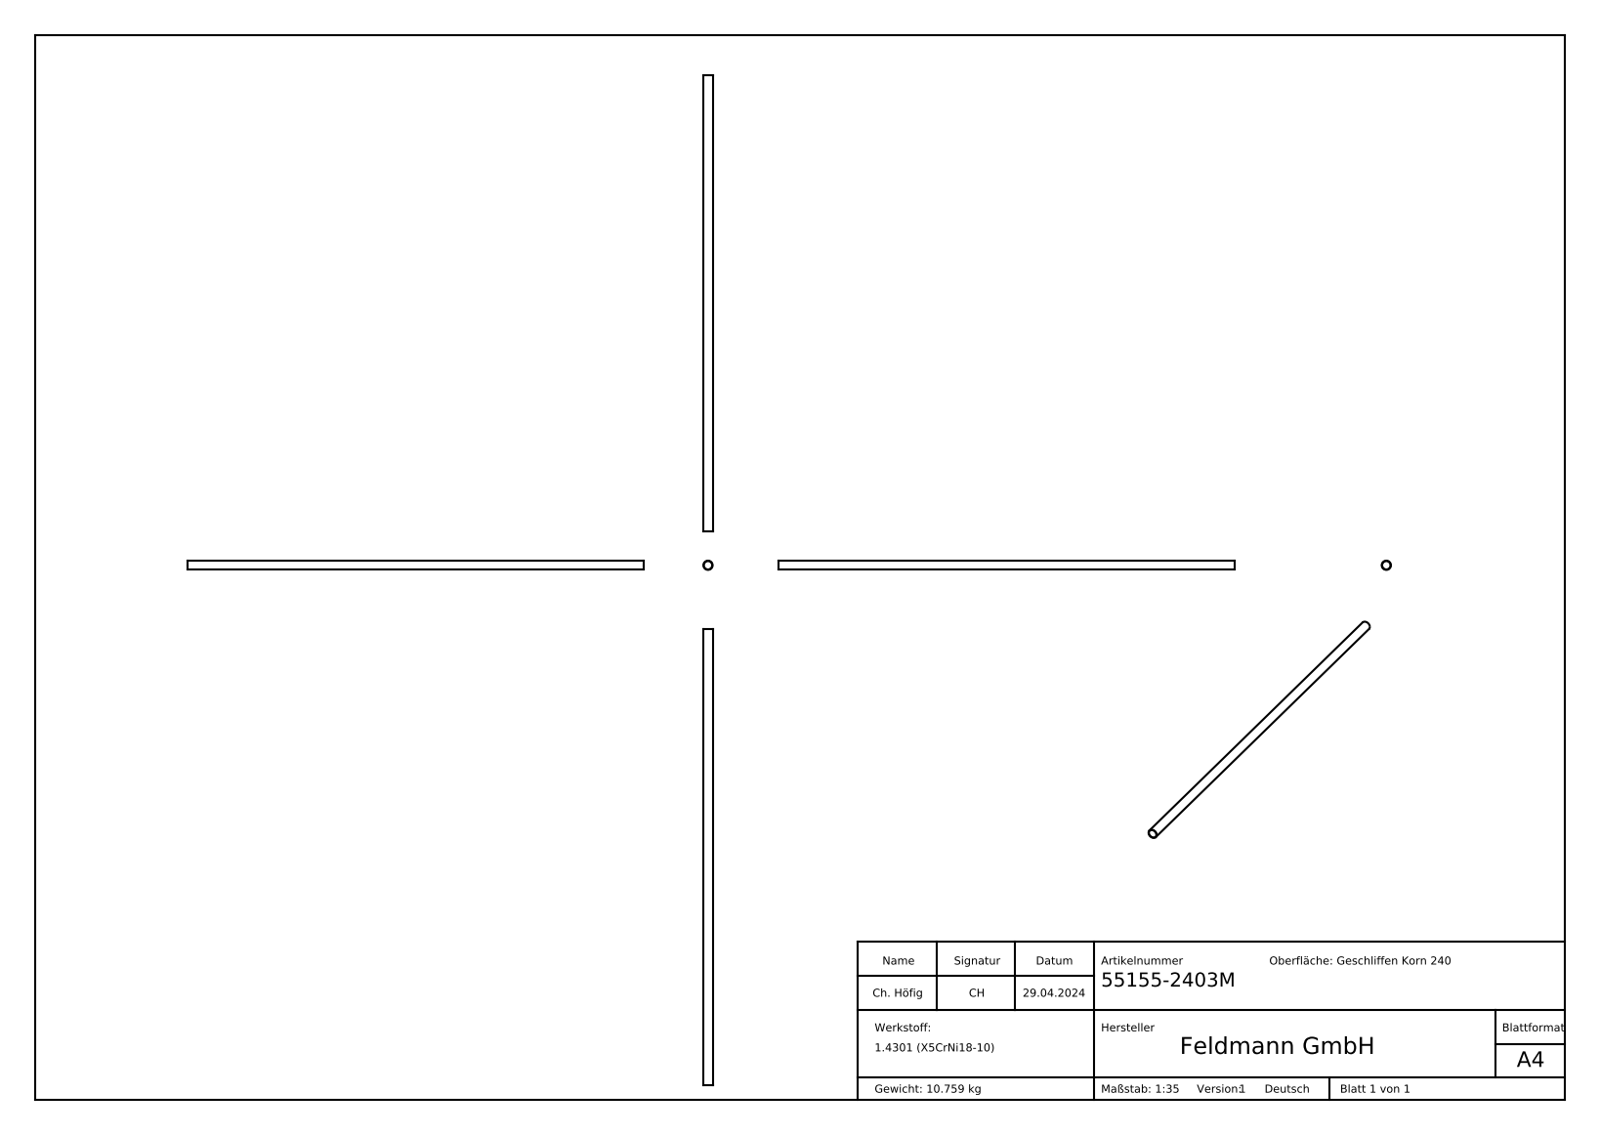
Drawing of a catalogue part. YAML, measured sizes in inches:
part_name: "55155-2403M"
step_written_by: "SolidWorks 2018 (CONFIG_CONTROL_DESIGN)"
units: inches
bodies: {solids: 1, faces: 303, planar: 147, cylindrical: 27, other: 129}
overall_size: [118.11, 2.374, 2.374]
volume: 83.11
surface_area: 1690
round_holes:
  - {diameter: 2.177, count: 1}
round_bosses_or_shafts:
  - {diameter: 2.374, count: 1}
partial_cylinders:
  - {radius: 1.093, count: 1}
face_to_face_distances: [118.11, 0.062, 0.07, 0.095, 0.103, 0.031, 0.088, 0.029, 0.096, 0.019]
